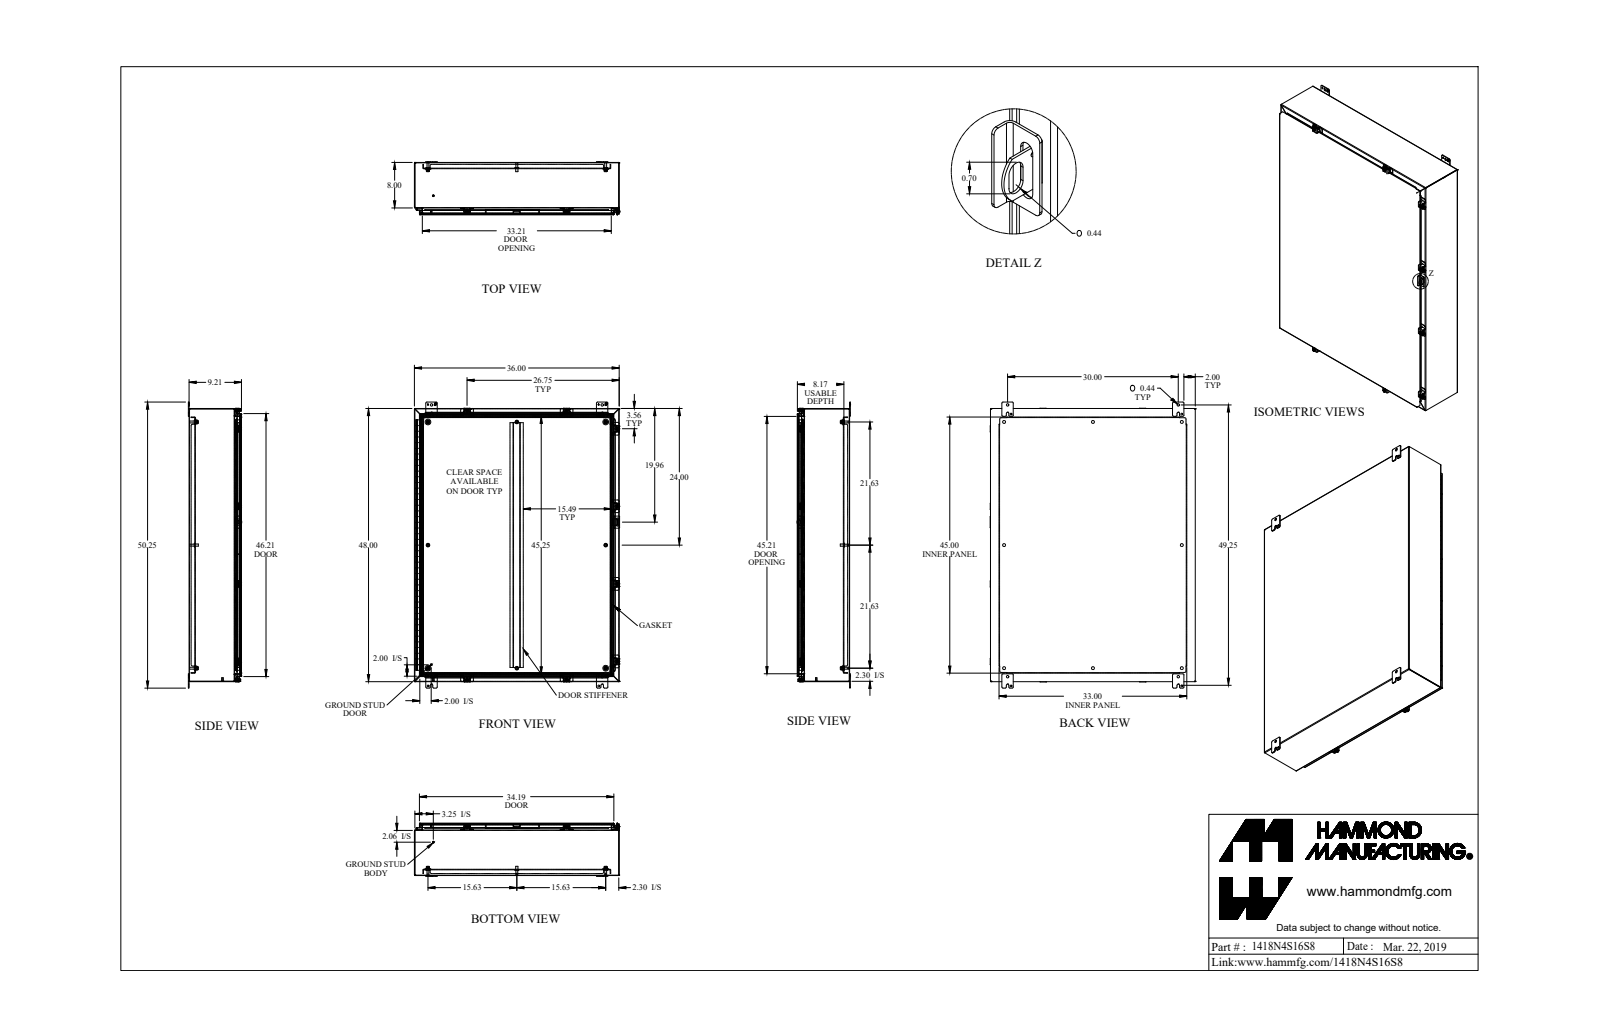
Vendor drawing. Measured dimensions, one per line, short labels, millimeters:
name: 1418N4S16S8_Default
written by: SolidWorks 2019 (CONFIG_CONTROL_DESIGN)
unit: mm
bodies: 64 solids, 2195 faces (1140 planar, 873 cylindrical, 182 other)
size: 1276.4 × 916 × 238.1
volume: 9 182 000 mm³; area: 9 386 000 mm²
holes: 8× ⌀5.4, 8× ⌀6.7, 8× ⌀9.5, 8× ⌀12.7, 4× ⌀7.8, 4× ⌀8, 4× ⌀11.1, 4× ⌀11.3, 1× ⌀2.8, 1× ⌀3.2
bosses: 8× ⌀16.5, 8× ⌀12.7, 8× ⌀9.9, 8× ⌀9.5, 8× ⌀8.4, 8× ⌀6.2, 4× ⌀25.4, 2× ⌀8
rounds: 44× R6.4, 39× R1.2, 39× R3.6, 30× R4.8, 24× R0.9, 24× R2.7, 16× R3.6, 14× R3.2
face distances: 1.8, 230.3, 232.1, 232.1, 2.4, 1.8, 233.9, 23.8, 25.6, 205.9
hole spacings: 965.3, 1308.3, 182.8, 396.9, 549.3, 621.5, 1165.7, 1168
